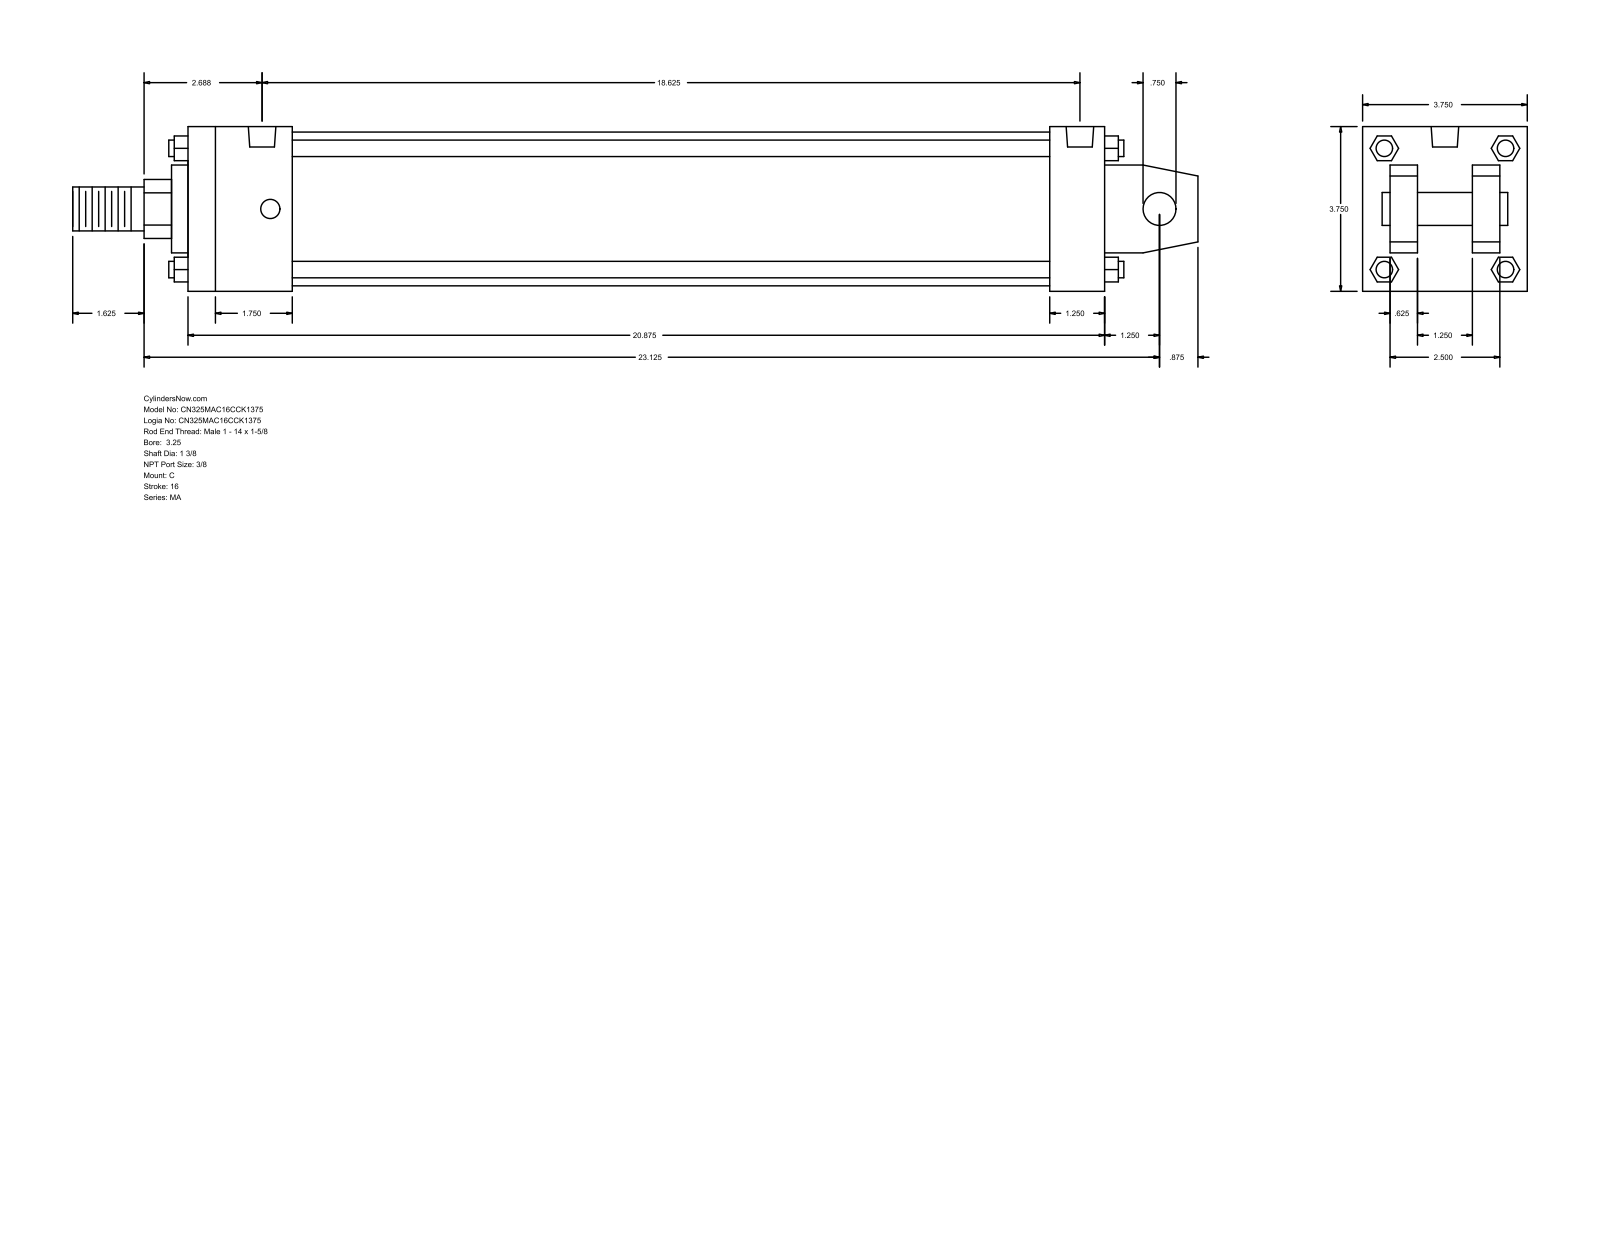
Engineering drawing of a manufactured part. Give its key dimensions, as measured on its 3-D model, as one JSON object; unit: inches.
{"part_name": "MA_C__0325_1.375", "step_written_by": "GSSL Pune (CONFIG_CONTROL_DESIGN)", "units": "inches", "bodies": {"solids": 0, "faces": 139, "planar": 108, "cylindrical": 31, "other": 0}, "overall_size": [25.625, 3.75, 3.75], "round_holes": [[0.437, 4], [0.627, 2]], "round_bosses_or_shafts": [[0.375, 4], [3.5, 1], [2, 1], [1.375, 1], [1, 1], [0.75, 1]], "partial_cylinders_radius": [[0.672, 1]], "face_to_face_distances": [3.75, 0.625, 1.25, 2.5, 20.875, 3.125, 1.875, 19.625, 2.375, 17.25], "hole_center_spacings": [18.25, 0.187, 0.188, 18.437, 18.438, 18.625]}
